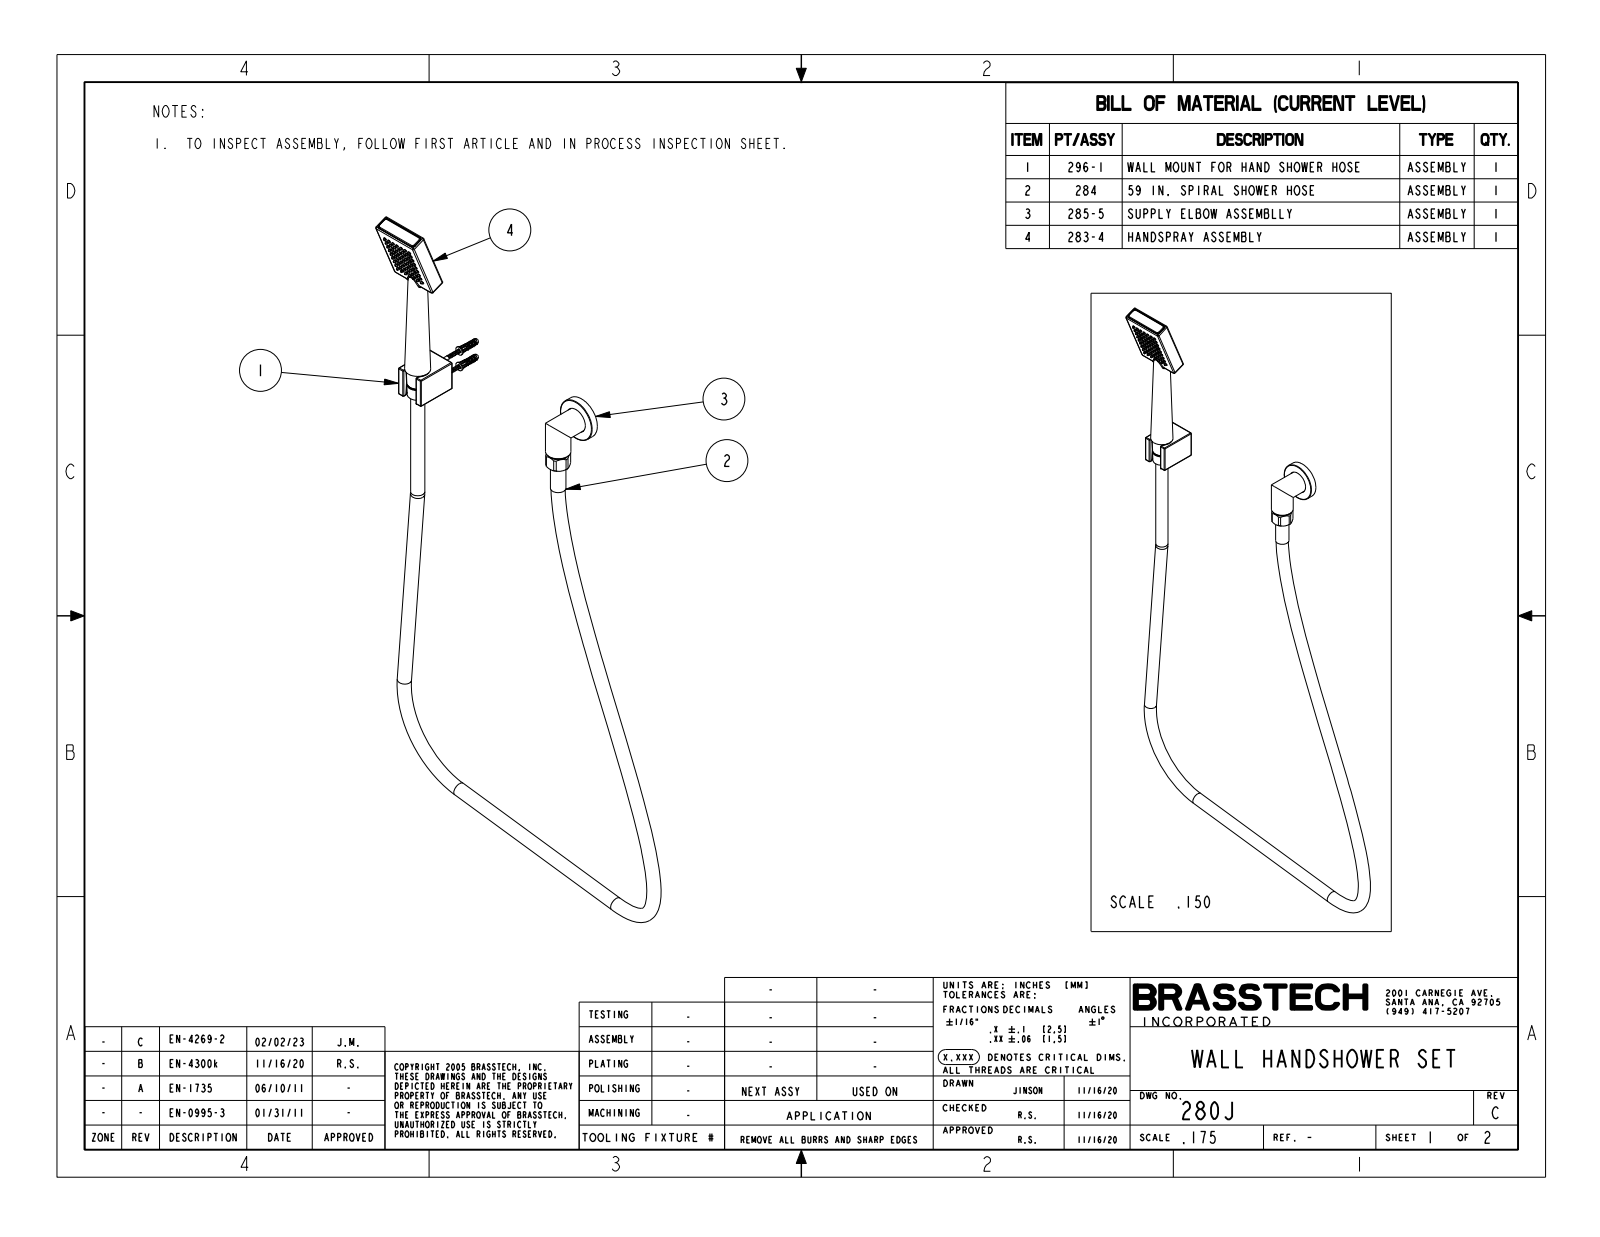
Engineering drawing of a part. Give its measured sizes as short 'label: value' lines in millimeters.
name: 280J
written by: CREO PARAMETRIC BY PTC INC, 2019352 (CONFIG_CONTROL_DESIGN)
unit: mm
bodies: 3 solids, 676 faces (162 planar, 316 cylindrical, 198 other)
size: 703.6 × 362.6 × 66
volume: 400 700 mm³; area: 98 000 mm²
holes: 63× ⌀0.8
bosses: 63× ⌀2.8, 3× ⌀14.2, 2× ⌀25.4, 1× ⌀44.5, 1× ⌀21.2, 1× ⌀19.1, 1× ⌀18.5, 1× ⌀15.5
rounds: 22× R0.8, 10× R1.3, 2× R2, 1× R12.5
face distances: 16.5, 31.8, 11.1, 42.8, 54, 42.9, 11.1, 7.9, 1, 32.8
hole spacings: 8.3, 13.4, 16.5, 31, 6.1, 12.2, 25, 5.6
